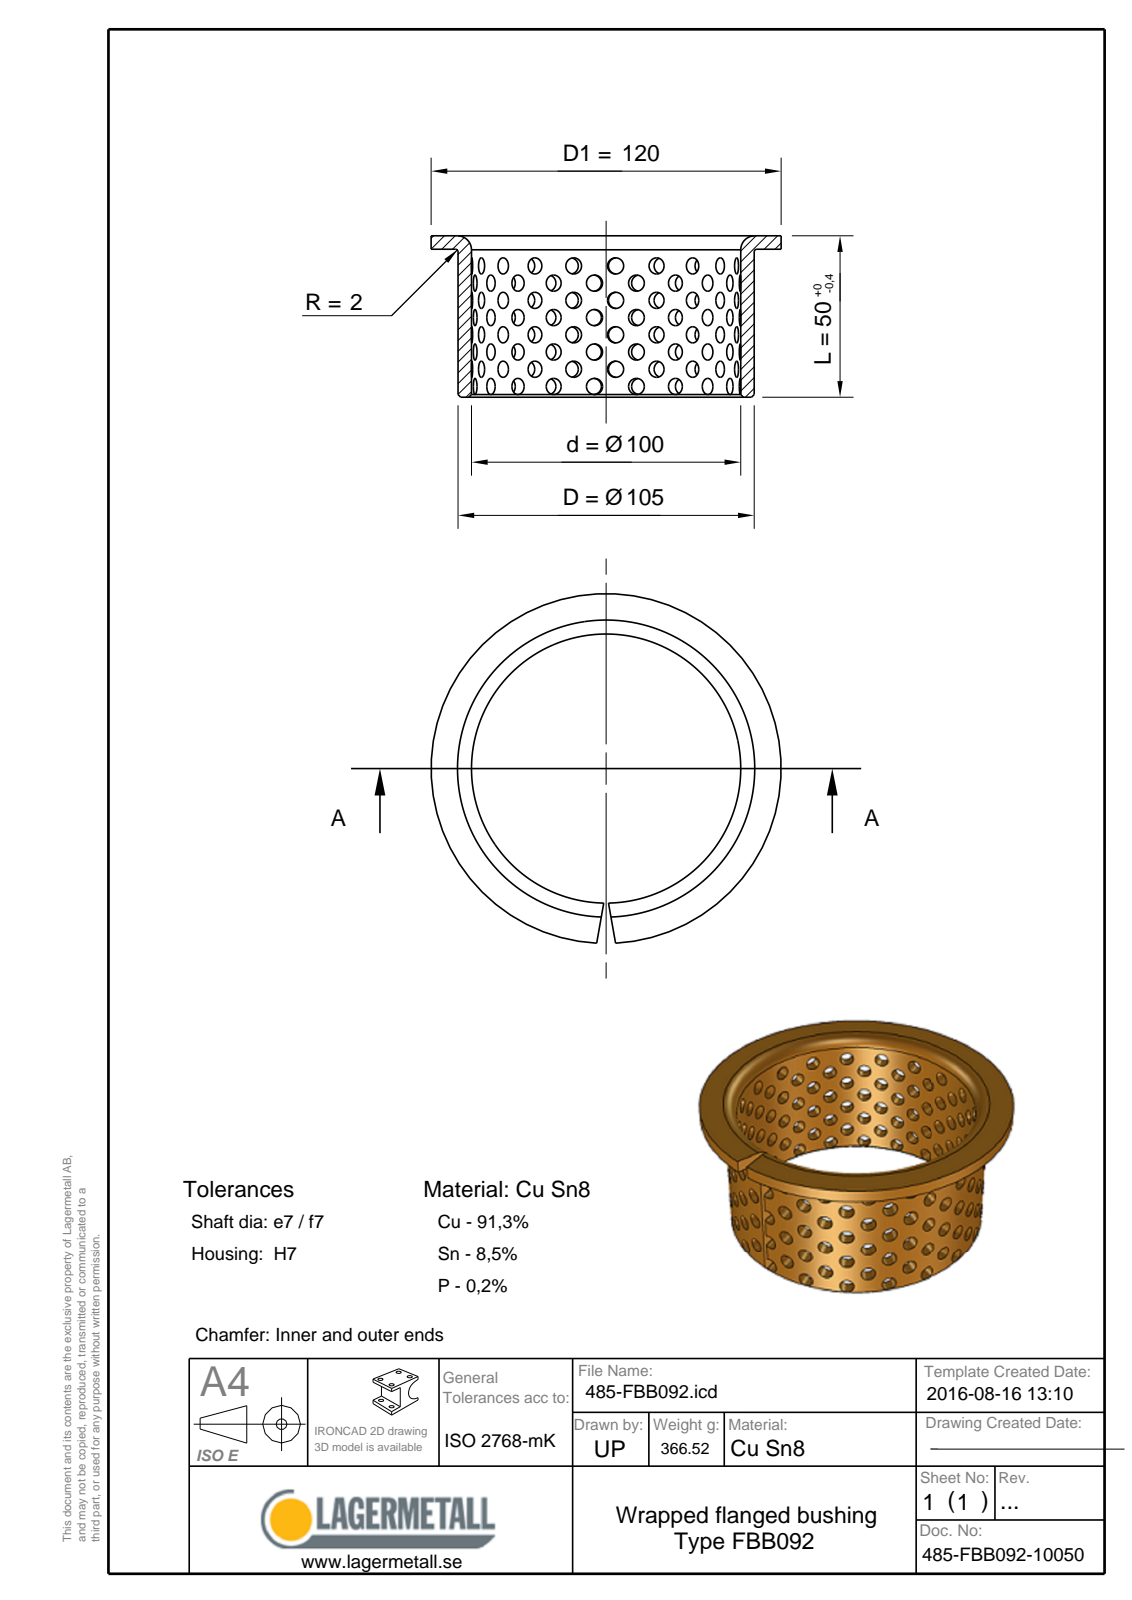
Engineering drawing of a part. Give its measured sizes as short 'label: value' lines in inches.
name: 485-FBB092-10050
written by: Spatial InterOp 3D (CONFIG_CONTROL_DESIGN)
unit: in
bodies: 1 solid, 12 faces (5 planar, 3 cylindrical, 4 other)
size: 4.724 × 4.723 × 1.969
volume: 2.761 in³; area: 59.08 in²
holes: 1× ⌀3.937
bosses: 1× ⌀4.724, 1× ⌀4.134
face distances: 0.098, 1.87, 1.969
